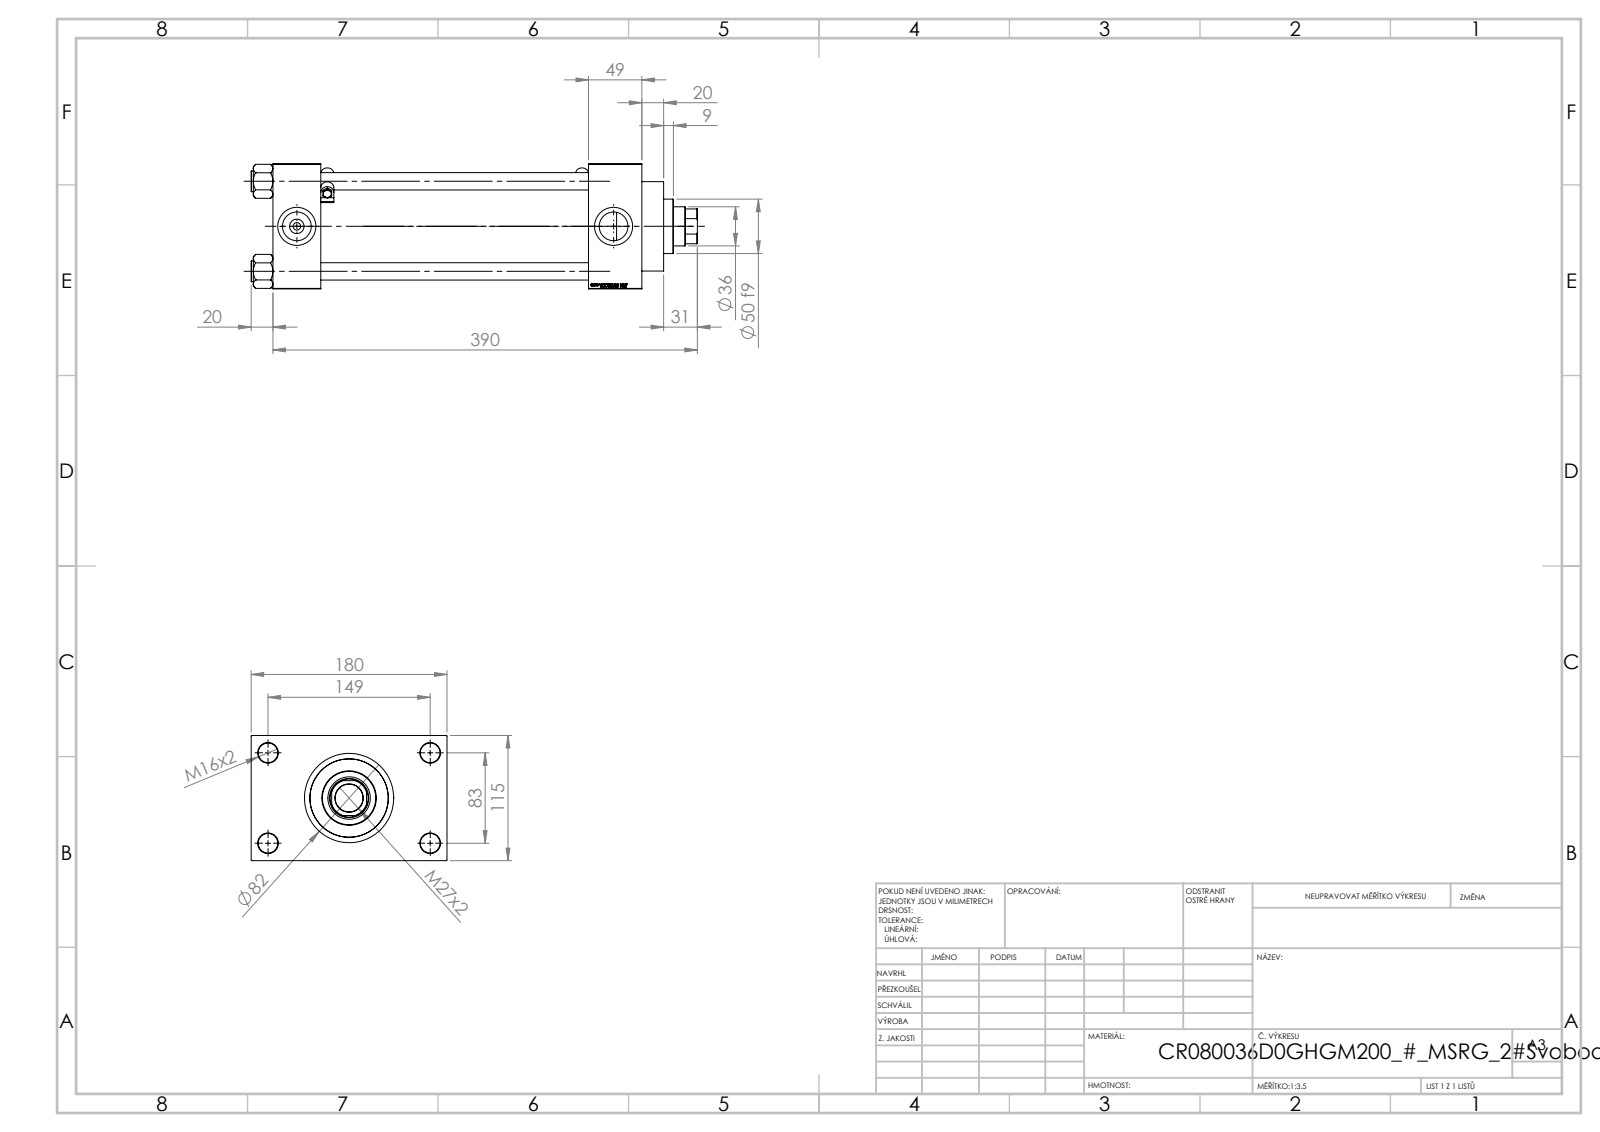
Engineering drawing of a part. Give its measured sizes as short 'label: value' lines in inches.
name: MSRF_MSRG1; V215CR_VCP_D; NUT_M5_D; V215_VC_A (+2 more)
written by: SolidWorks 2019 (CONFIG_CONTROL_DESIGN)
unit: in
bodies: 13 solids, 1215 faces (581 planar, 116 cylindrical, 518 other)
size: 16.142 × 7.087 × 4.528
volume: 149.9 in³; area: 700.2 in²
holes: 4× ⌀0.63, 4× ⌀0.709, 2× ⌀0.276, 2× ⌀1.041, 2× ⌀1.378, 1× ⌀1.004, 1× ⌀1.417, 1× ⌀1.535, 1× ⌀2.402, 1× ⌀2.835, 1× ⌀3.15
bosses: 4× ⌀0.748, 2× ⌀0.197, 2× ⌀0.098, 1× ⌀3.386, 1× ⌀3.228, 1× ⌀1.969
rounds: 12× R0.02, 4× R0.236, 1× R0.689
face distances: 4.528, 9.685, 11.614, 1.929, 1.732, 11.417, 13.346, 1.28, 5.807, 7.087
hole spacings: 1.305, 2.302, 3.256, 3.357, 3.513, 4.561, 5.607, 3.268
